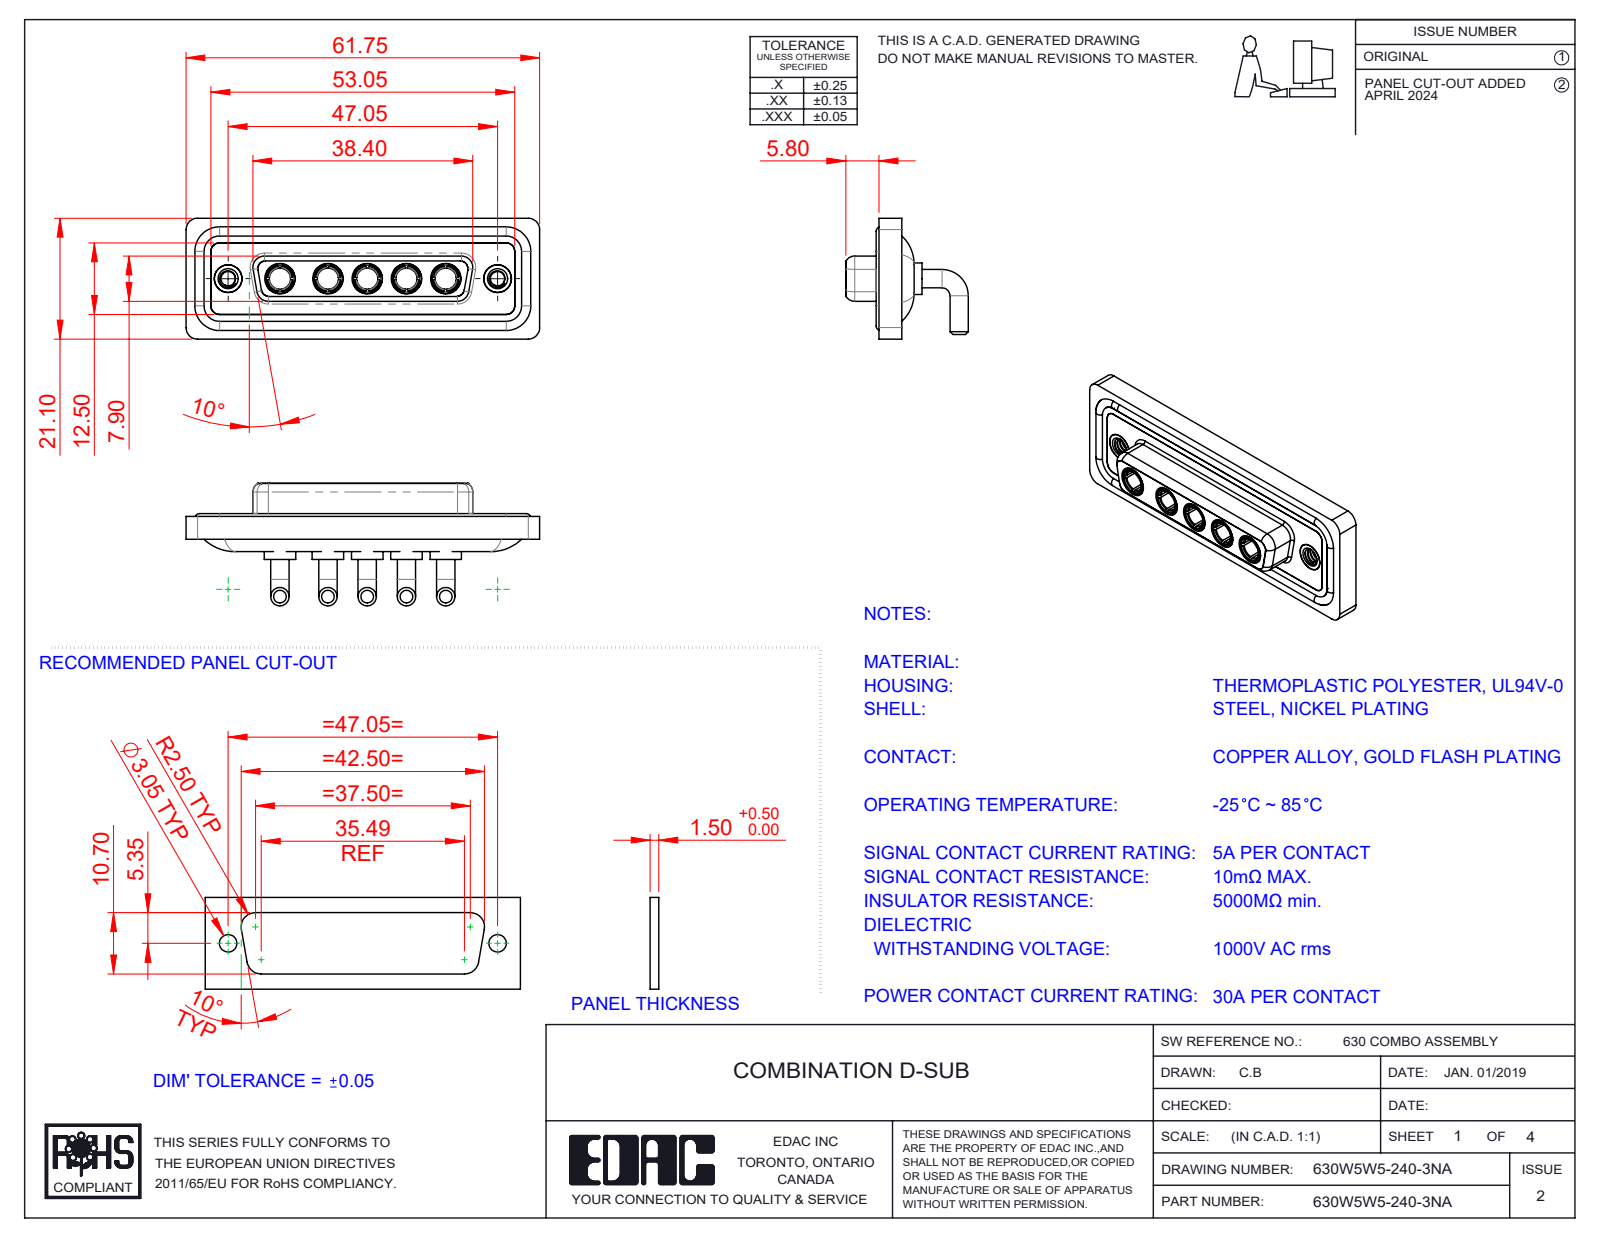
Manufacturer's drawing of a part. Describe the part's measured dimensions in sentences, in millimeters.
The part is named "630W5W5-240-3NA; 630Combo Shell Rear_25 Contacts; 630Combo Threaded Rivet_A; 630Combo Shell Front_25 Contacts (+3 more)". Its 3-D file was written by "SolidWorks 2023 (CONFIG_CONTROL_DESIGN)". It is 17 solids with 770 faces: 250 planar, 311 cylindrical and 209 other. Overall it measures 61.75 by 21.4 by 21.1 millimeters. Its volume is 8 568 cubic millimeters and its surface area 13 908 square millimeters. Round holes: 7 of diameter 4.85, 5 of diameter 3.7, 5 of diameter 5.3, 2 of diameter 2.5, 2 of diameter 4, 2 of diameter 4.05, 2 of diameter 5. Round bosses or shafts: 10 of diameter 3.2, 5 of diameter 5.5, 5 of diameter 5.2, 5 of diameter 4.96, 5 of diameter 4.75, 5 of diameter 3.75, 4 of diameter 1.6, 2 of diameter 4.95. Partial cylindrical surfaces (rounded edges, fillets, slot ends): 18 of radius 1.5, 18 of radius 2, 8 of radius 1.35, 8 of radius 1.6, 5 of radius 2.1, 4 of radius 0.25, 4 of radius 0.5, 4 of radius 0.6. The main face-to-face distances are 0.4, 1.8, 4.1, 1.1, 1.5, 2.5, 3.1, 3.7, 1.6, 2.9. The hole center spacings are 6.86, 9.04, 38.01, 6.87, 8.38, 13.72, 13.73, 15.25.
